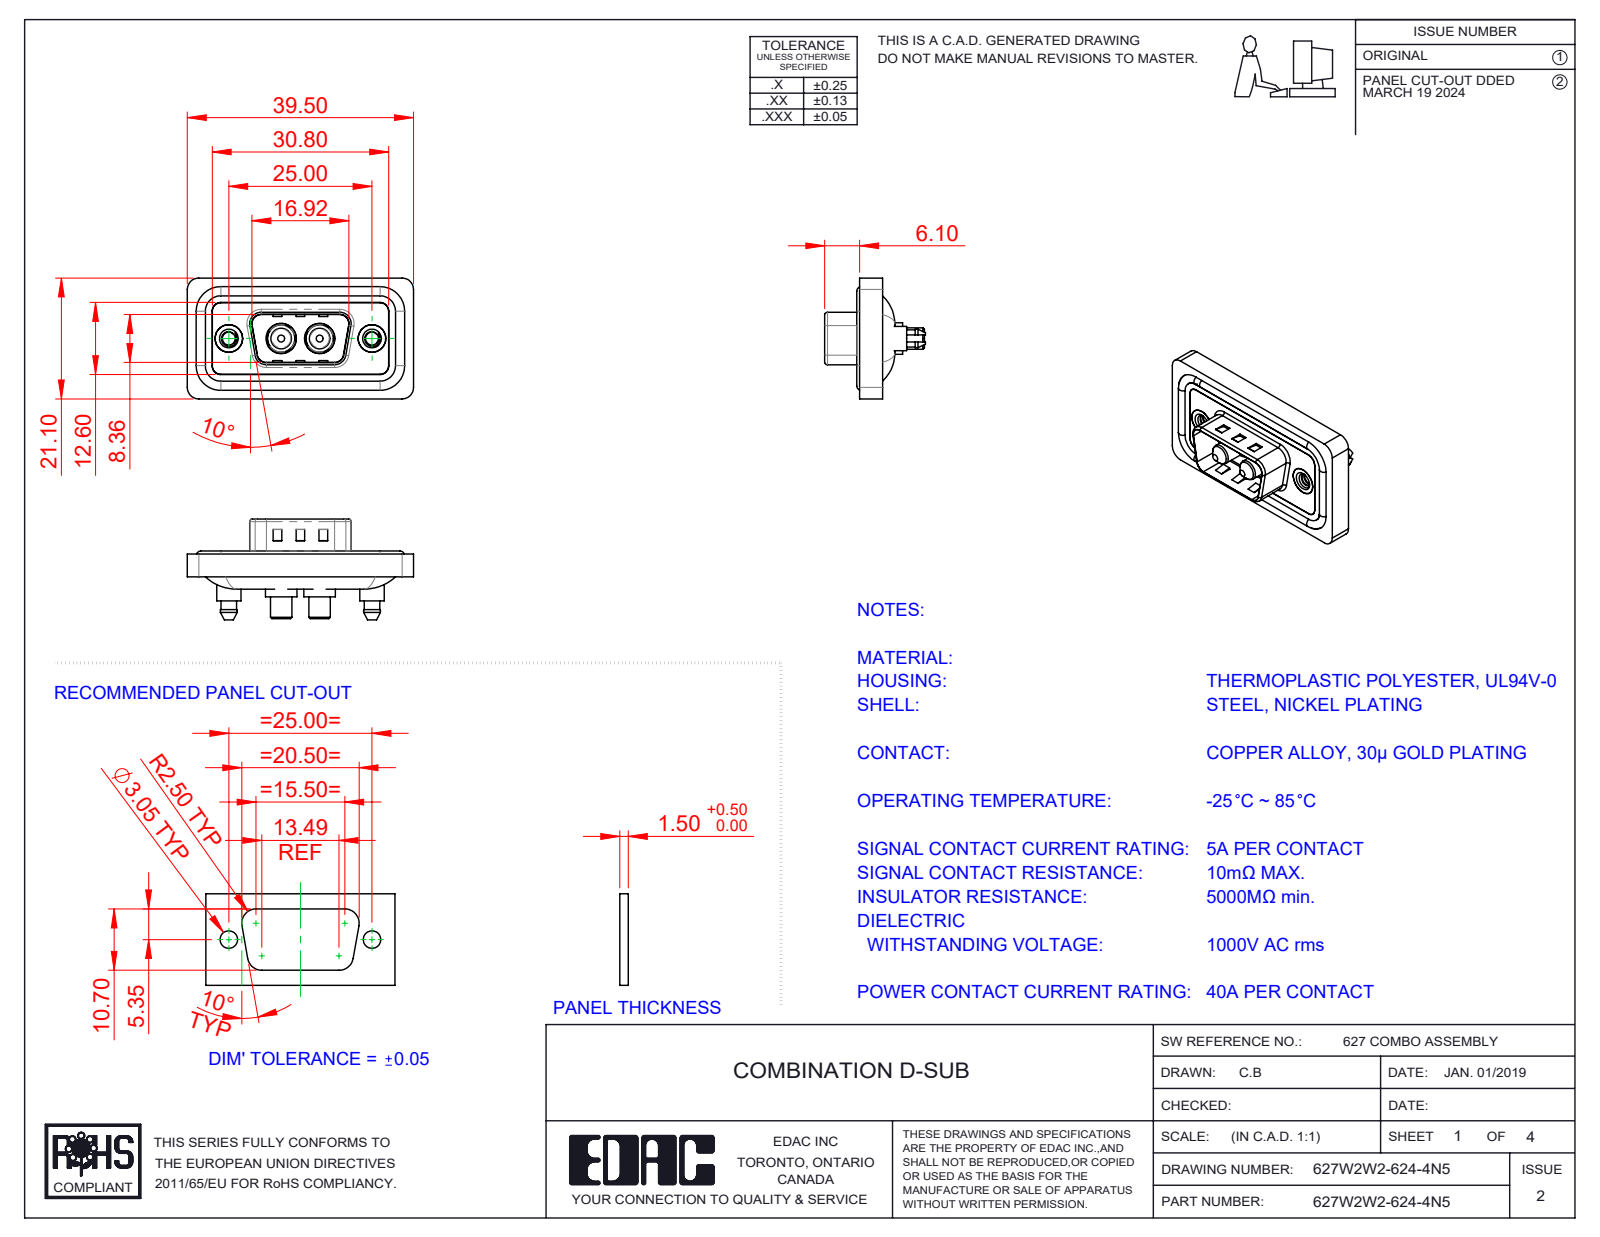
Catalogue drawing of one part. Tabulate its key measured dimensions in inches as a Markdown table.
| quantity | value |
| --- | --- |
| part name | Power Pin_40A S; 627Combo Shell Front_09 Contacts; 627W2W2-624-4N5; 627Combo Housing_2W2 (+3 more) |
| STEP written by | SolidWorks 2023 (CONFIG_CONTROL_DESIGN) |
| units | inches |
| bodies | 11 solids, 539 faces (181 planar, 250 cylindrical, 108 other) |
| overall size | 1.555 × 0.831 × 0.693 |
| volume | 0.283 in³ |
| surface area | 11.38 in² |
| round holes (diameter × count) | 0.089 × 2, 0.157 × 2, 0.189 × 2, 0.191 × 2, 0.197 × 2, 0.209 × 2 |
| round bosses / shafts (diameter × count) | 0.063 × 4, 0.217 × 2, 0.213 × 2, 0.205 × 2, 0.193 × 2, 0.187 × 2, 0.167 × 2, 0.148 × 2 |
| partial cylindrical surfaces (radius × count) | 0.059 × 24, 0.079 × 18, 0.063 × 10, 0.02 × 8, 0.01 × 4, 0.024 × 4, 0.026 × 4, 0.035 × 4 |
| main face-to-face distances | 0.016, 0.043, 0.114, 0.122, 0.02, 0.063, 0.059, 0.157, 0.028, 0.098 |
| hole center spacings | 0.36, 0.624, 0.265, 0.984 |
